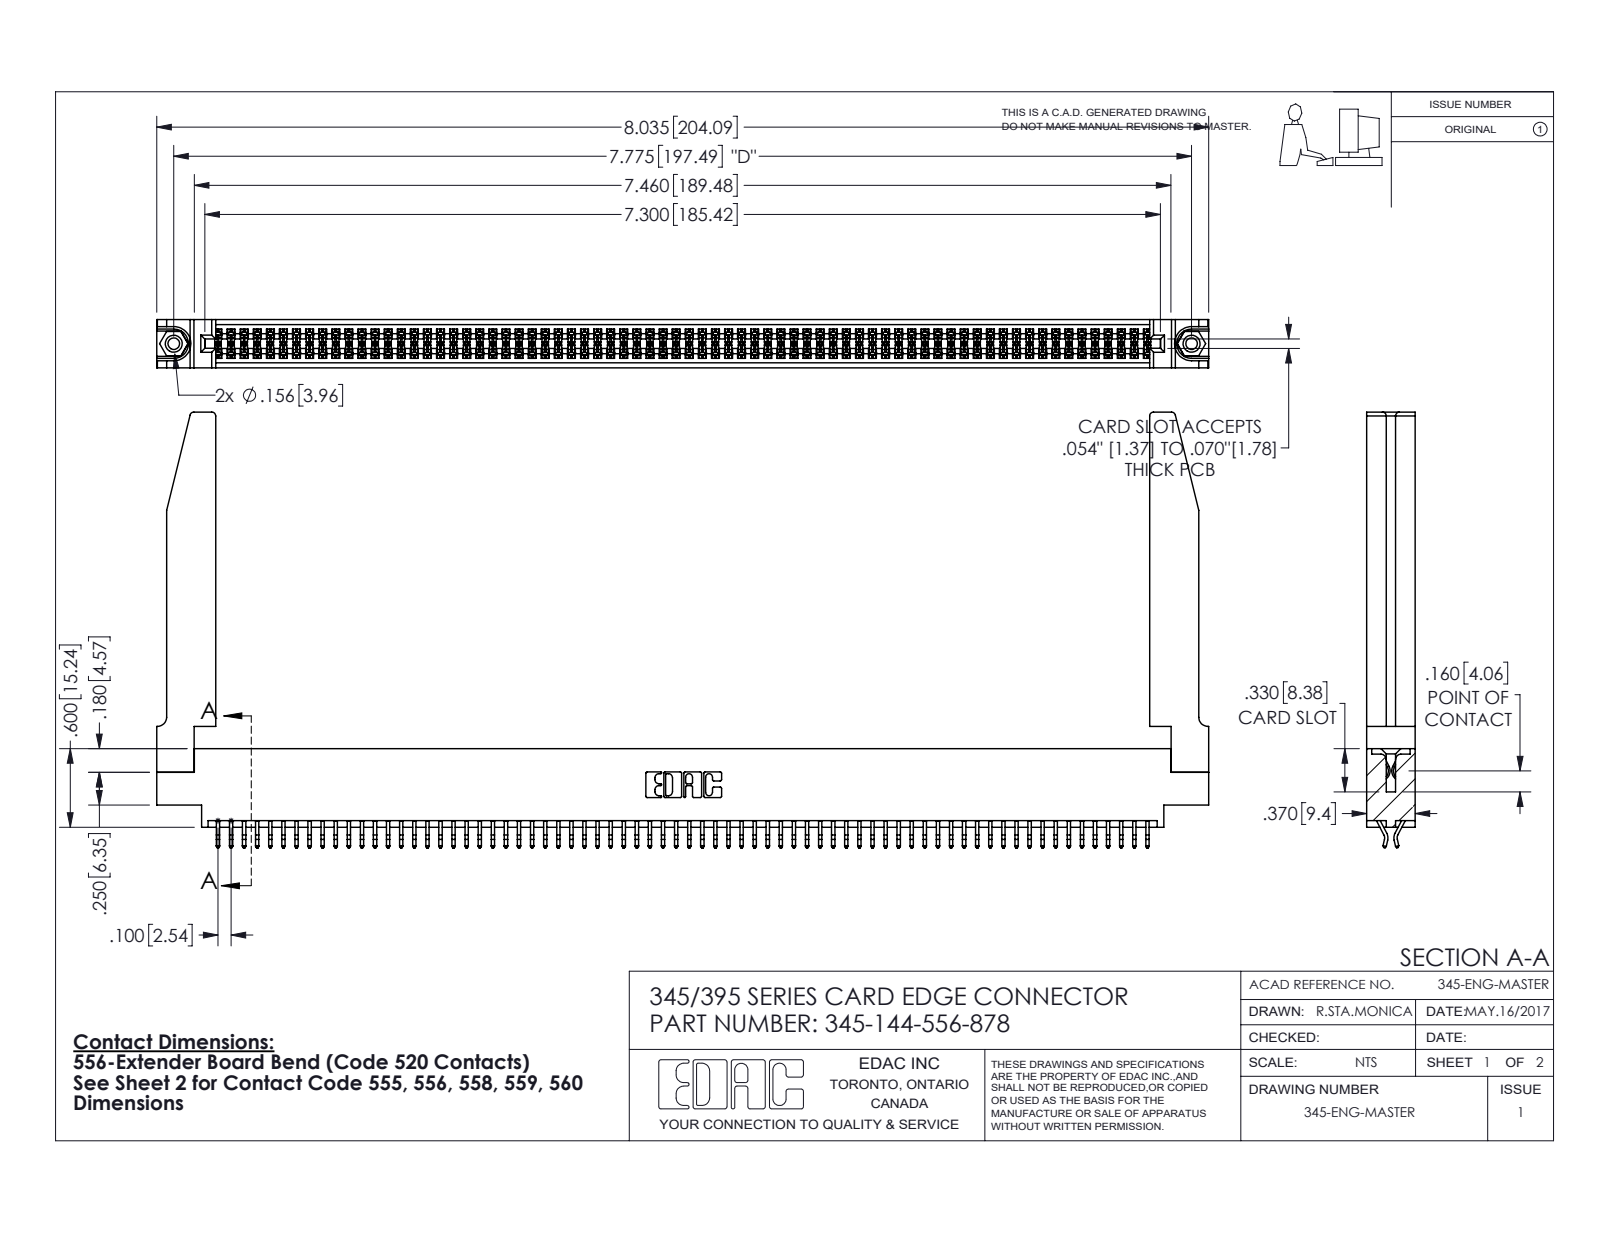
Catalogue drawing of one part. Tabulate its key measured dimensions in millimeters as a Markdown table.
| quantity | value |
| --- | --- |
| part name | 345-220-078_345-220-078; 345-144-556-878; 345-250-001_345-250-001-102; 345-292-001_556 Tail (+1 more) |
| STEP written by | SolidWorks 2016 (CONFIG_CONTROL_DESIGN) |
| units | millimeters |
| bodies | 149 solids, 8428 faces (5554 planar, 2822 cylindrical, 52 other) |
| overall size | 204.1 × 84.5 × 9.4 |
| volume | 27 760 mm³ |
| surface area | 36 980 mm² |
| round holes (diameter × count) | 2.3 × 2, 3.2 × 2, 4 × 2, 1.6 × 1 |
| round bosses / shafts (diameter × count) | 3.9 × 2 |
| partial cylindrical surfaces (radius × count) | 0.2 × 216, 0.3 × 22, 0.8 × 8, 0.2 × 6, 0.8 × 6, 0.7 × 3, 0.3 × 2, 0.4 × 2 |
| main face-to-face distances | 1.8, 7.6, 9.4, 0.6, 2.5, 6.9, 5.1, 5.7, 4.4, 3.8 |
| hole center spacings | 6.9, 191.5, 197.5 |
